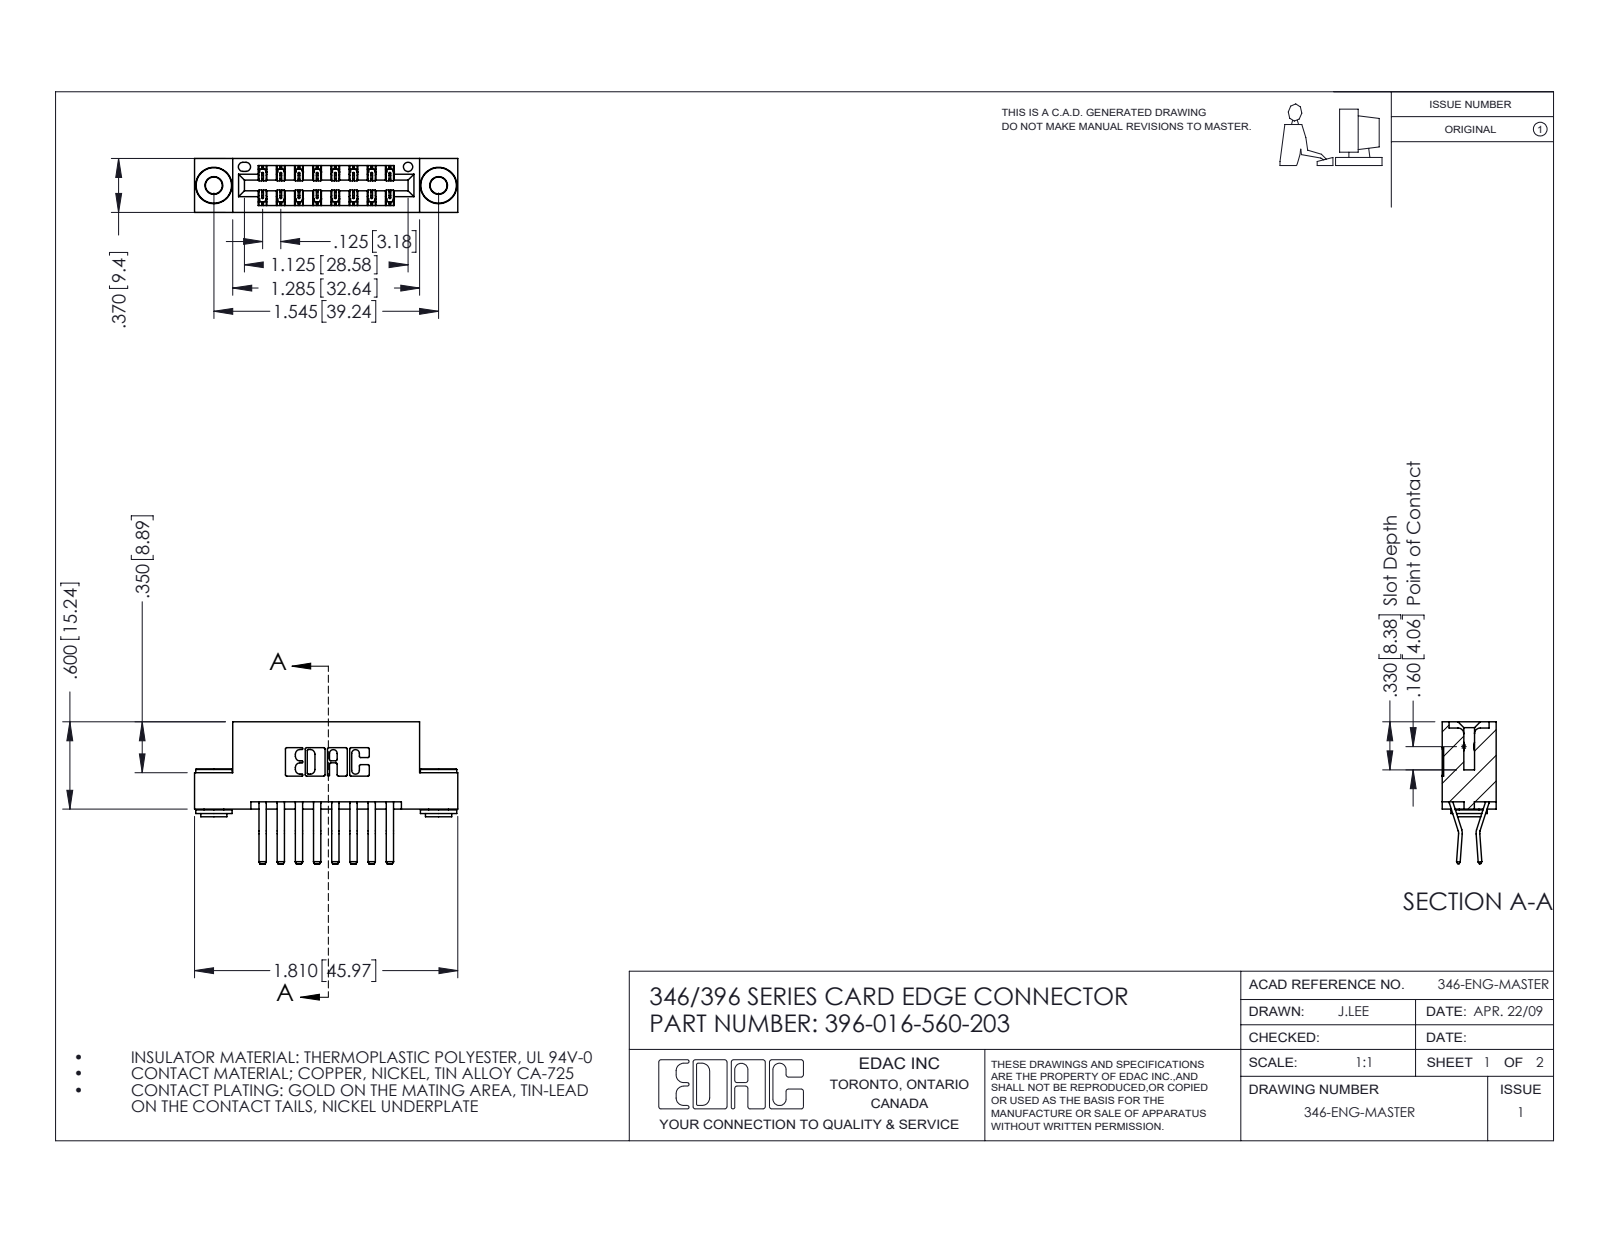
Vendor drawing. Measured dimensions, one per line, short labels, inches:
name: 345-250-002_345-250-002-102; 396-016-560-203; 346 Part_Flush Mounting Lugs - 0.156 Dia-TH; 345-292-001_560 Tail
written by: SolidWorks 2016 (CONFIG_CONTROL_DESIGN)
unit: in
bodies: 19 solids, 1024 faces (646 planar, 370 cylindrical, 8 other)
size: 1.81 × 0.975 × 0.37
volume: 0.265 in³; area: 9.191 in²
holes: 2× ⌀0.116, 2× ⌀0.156, 1× ⌀0.064
bosses: 2× ⌀0.25, 2× ⌀0.18, 2× ⌀0.136
rounds: 24× R0.006, 22× R0.01, 6× R0.007, 6× R0.031, 3× R0.026, 2× R0.01, 2× R0.014, 2× R0.022
face distances: 0.25, 0.048, 0.322, 0.37, 0.025, 0.5, 0.148, 0.222, 0.1, 0.174
hole spacings: 0.246, 1.341, 1.545
